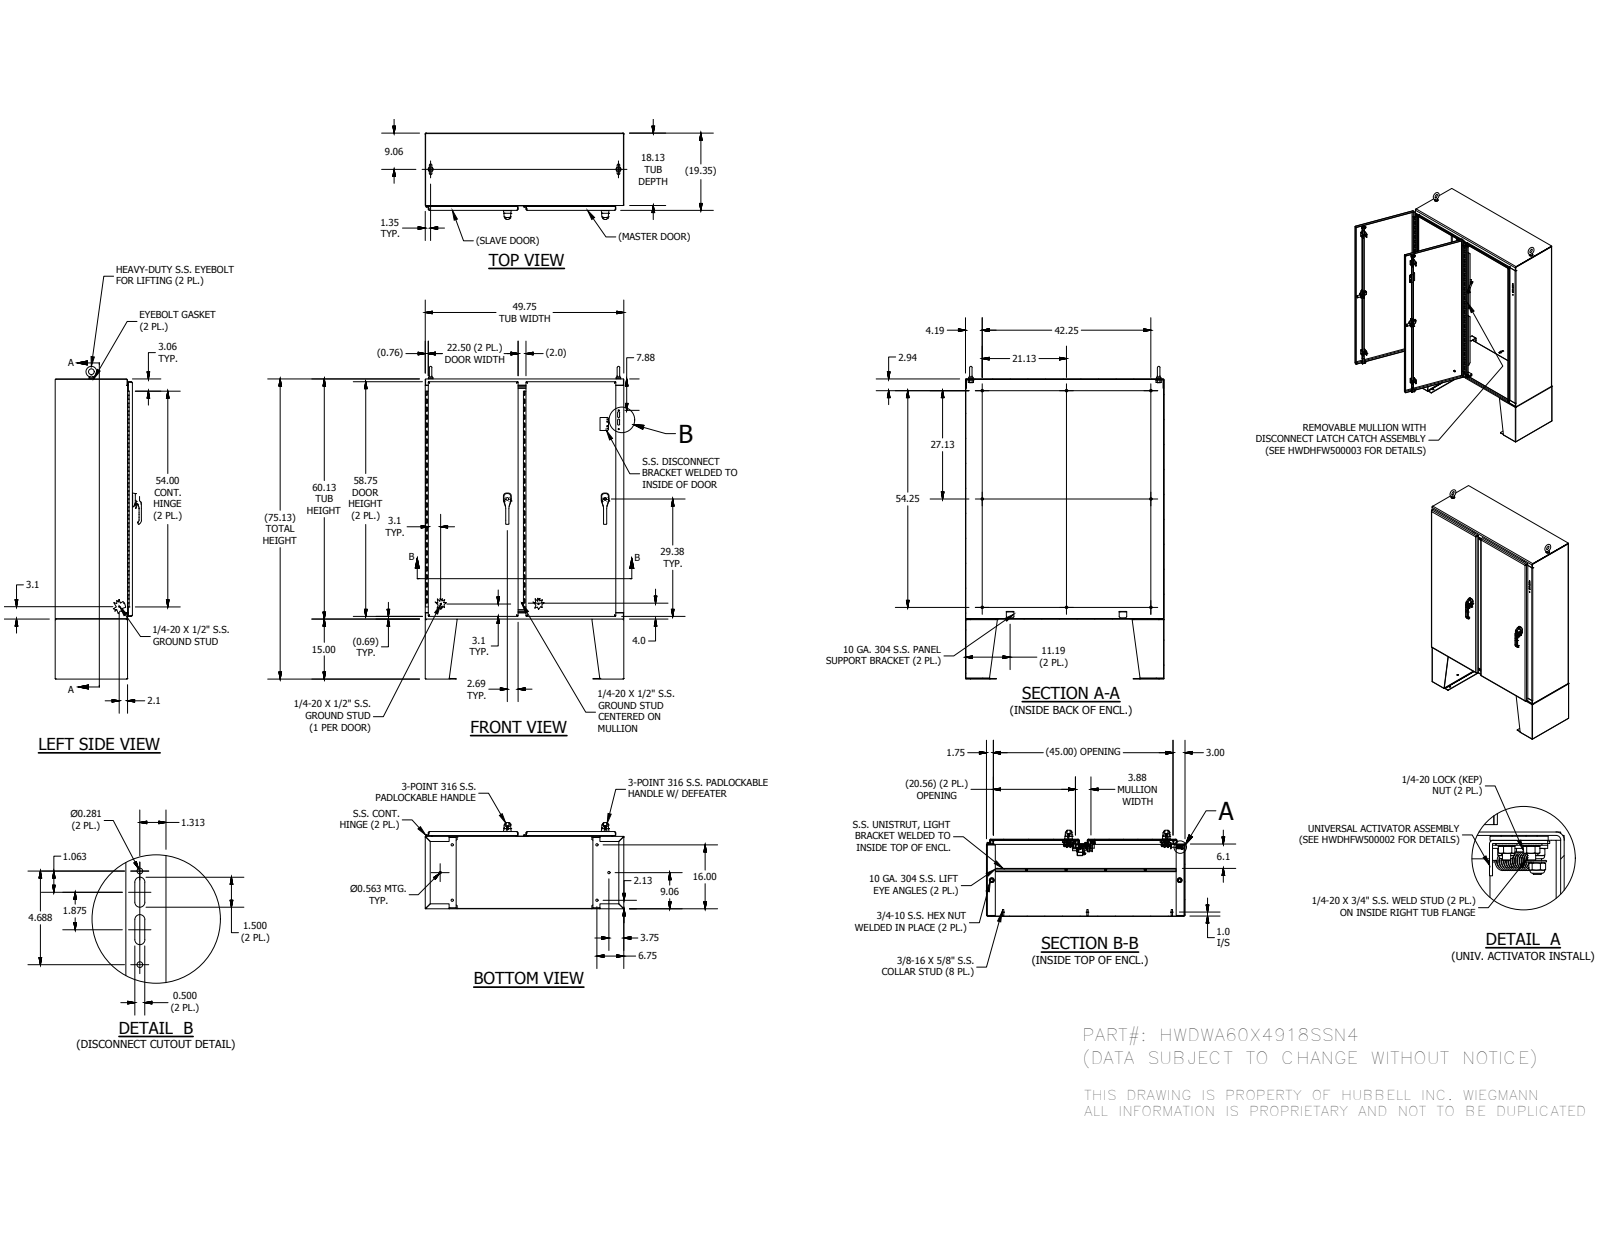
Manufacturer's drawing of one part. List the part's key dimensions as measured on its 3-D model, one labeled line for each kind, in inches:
Part name (STEP PRODUCT): WA60X4918SSN4BLR; WAX4918SSN4TOP; WAX4918SSN4BTM; HFW332010S (+8 more)
STEP written by: Autodesk Inventor 2016 (AUTOMOTIVE_DESIGN)
Units: inches
Bodies: 217 solids, 8968 faces (4124 planar, 3044 cylindrical, 1800 other)
Overall size (bounding box): 78.248 × 49.75 × 21.596
Volume: 1 430 in³ · Surface area: 27 300 in²
Round holes (diameter × count): ⌀0.25 ×18, ⌀0.375 ×18, ⌀0.563 ×18, ⌀0.187 ×9, ⌀0.19 ×8, ⌀0.196 ×8, ⌀0.262 ×8, ⌀0.289 ×8, ⌀0.335 ×8, ⌀0.38 ×8, ⌀0.281 ×7, ⌀0.156 ×6
Round bosses / shafts (diameter × count): ⌀0.25 ×20, ⌀0.33 ×18, ⌀0.625 ×13, ⌀0.337 ×12, ⌀0.375 ×11, ⌀0.563 ×9, ⌀0.28 ×8, ⌀1 ×6
Partial cylindrical surfaces — rounded edges, fillets, slot ends (radius × count): R0.02 ×359, R0.012 ×221, R0.02 ×192, R0.125 ×55, R0.019 ×42, R0.05 ×28, R0.079 ×28, R0.25 ×23
Main face-to-face distances: 0.104, 19.244, 19.14, 19.348, 49.646, 60.021, 0.125, 49.542, 49.75, 0.104
Hole centre spacings: 24.483, 0.38, 0.76, 1.195, 1.459, 5, 6.063, 6.845
